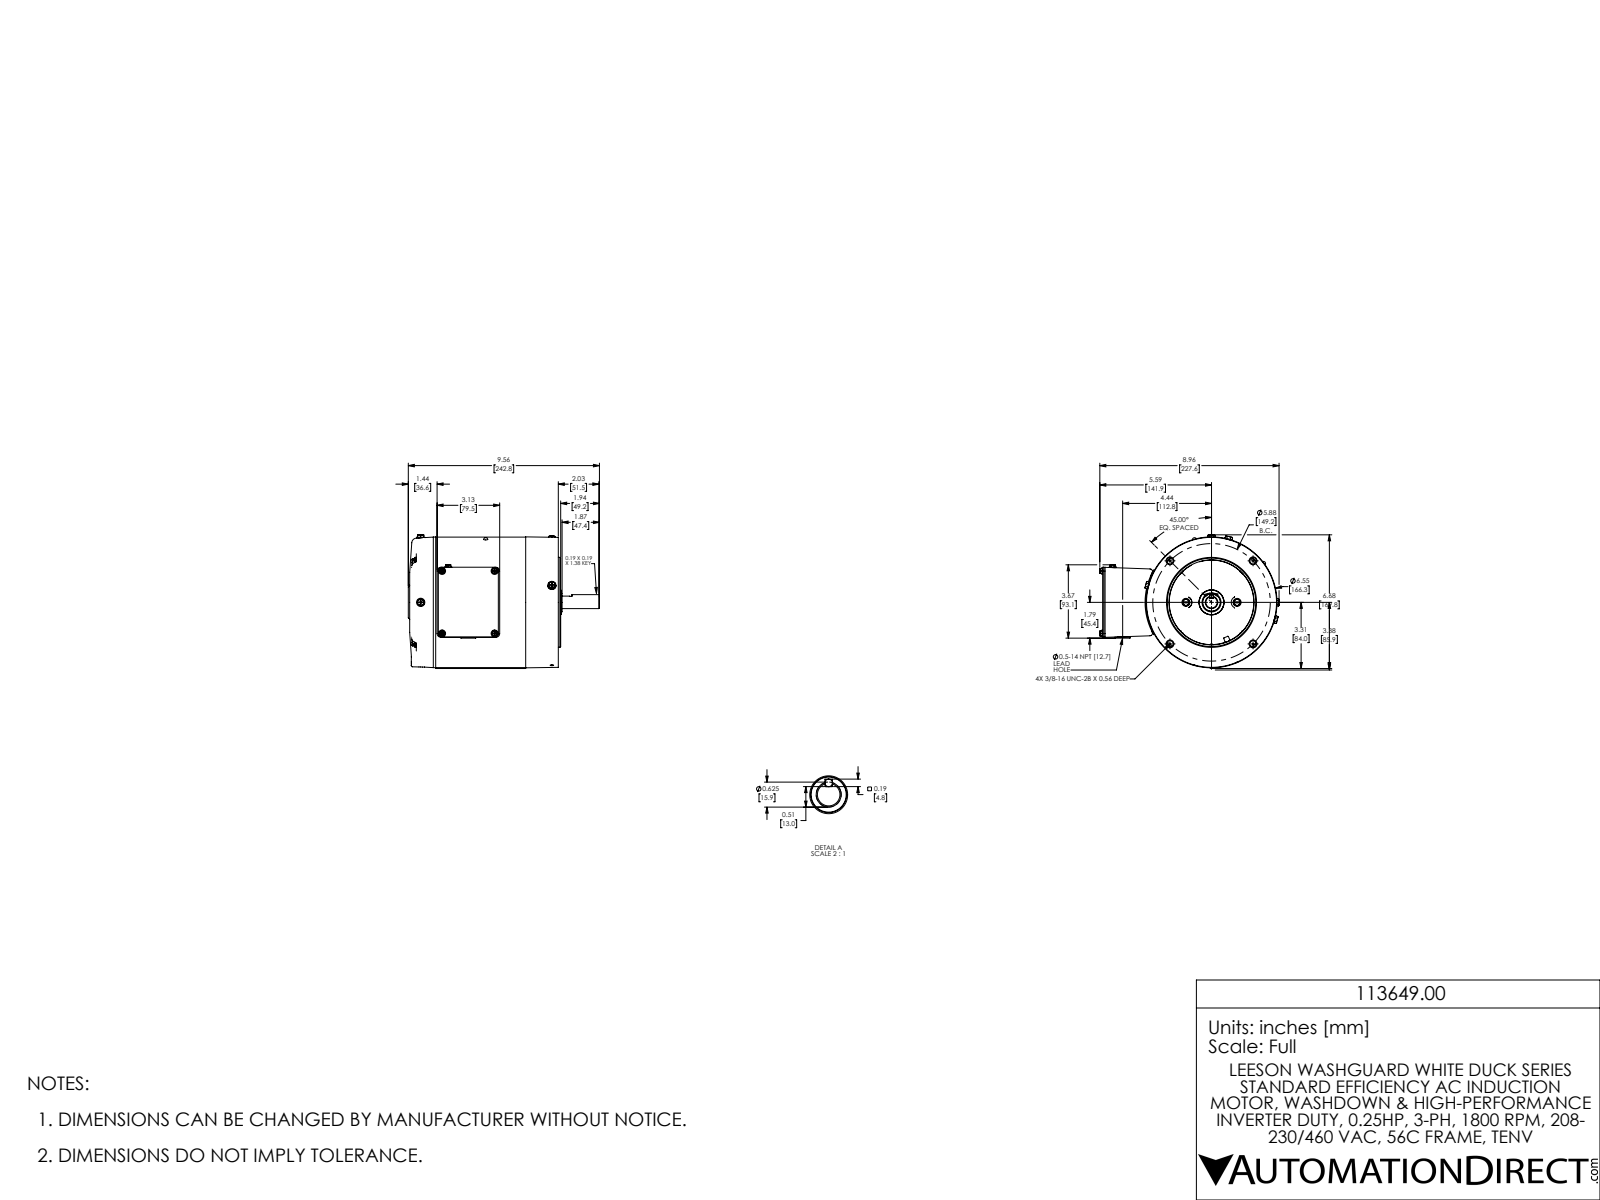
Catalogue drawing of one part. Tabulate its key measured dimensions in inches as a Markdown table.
| quantity | value |
| --- | --- |
| part name | 034960-450_Rev01_56C_0P25HP wo Front Bell COMPLETE A Coord |
| STEP written by | SolidWorks 2017 (AUTOMOTIVE_DESIGN) |
| units | inches |
| bodies | 36 solids, 3590 faces (847 planar, 549 cylindrical, 2194 other) |
| overall size | 9.557 × 8.962 × 6.684 |
| volume | 60.63 in³ |
| surface area | 660.8 in² |
| round holes (diameter × count) | 0.177 × 7, 0.19 × 7, 0.147 × 6, 0.159 × 4, 0.25 × 4, 0.26 × 4, 0.272 × 4, 0.313 × 4, 0.173 × 3, 0.103 × 2, 0.128 × 2, 0.21 × 2 |
| round bosses / shafts (diameter × count) | 0.19 × 11, 0.399 × 6, 0.414 × 5, 0.348 × 5, 0.164 × 5, 0.5 × 4, 0.166 × 4, 0.112 × 2 |
| partial cylindrical surfaces (radius × count) | 0.06 × 93, 0.03 × 61, 0.01 × 8, 0.19 × 8, 0.014 × 6, 0.043 × 6, 0.17 × 4, 0.058 × 3 |
| main face-to-face distances | 1.05, 0.063, 0.059, 0.122, 0.19, 0.12, 6.38, 7.43, 0.12, 7.21 |
| hole center spacings | 4.078, 0.11, 1.878, 2.095, 2.125, 2.193, 2.225, 2.63 |
